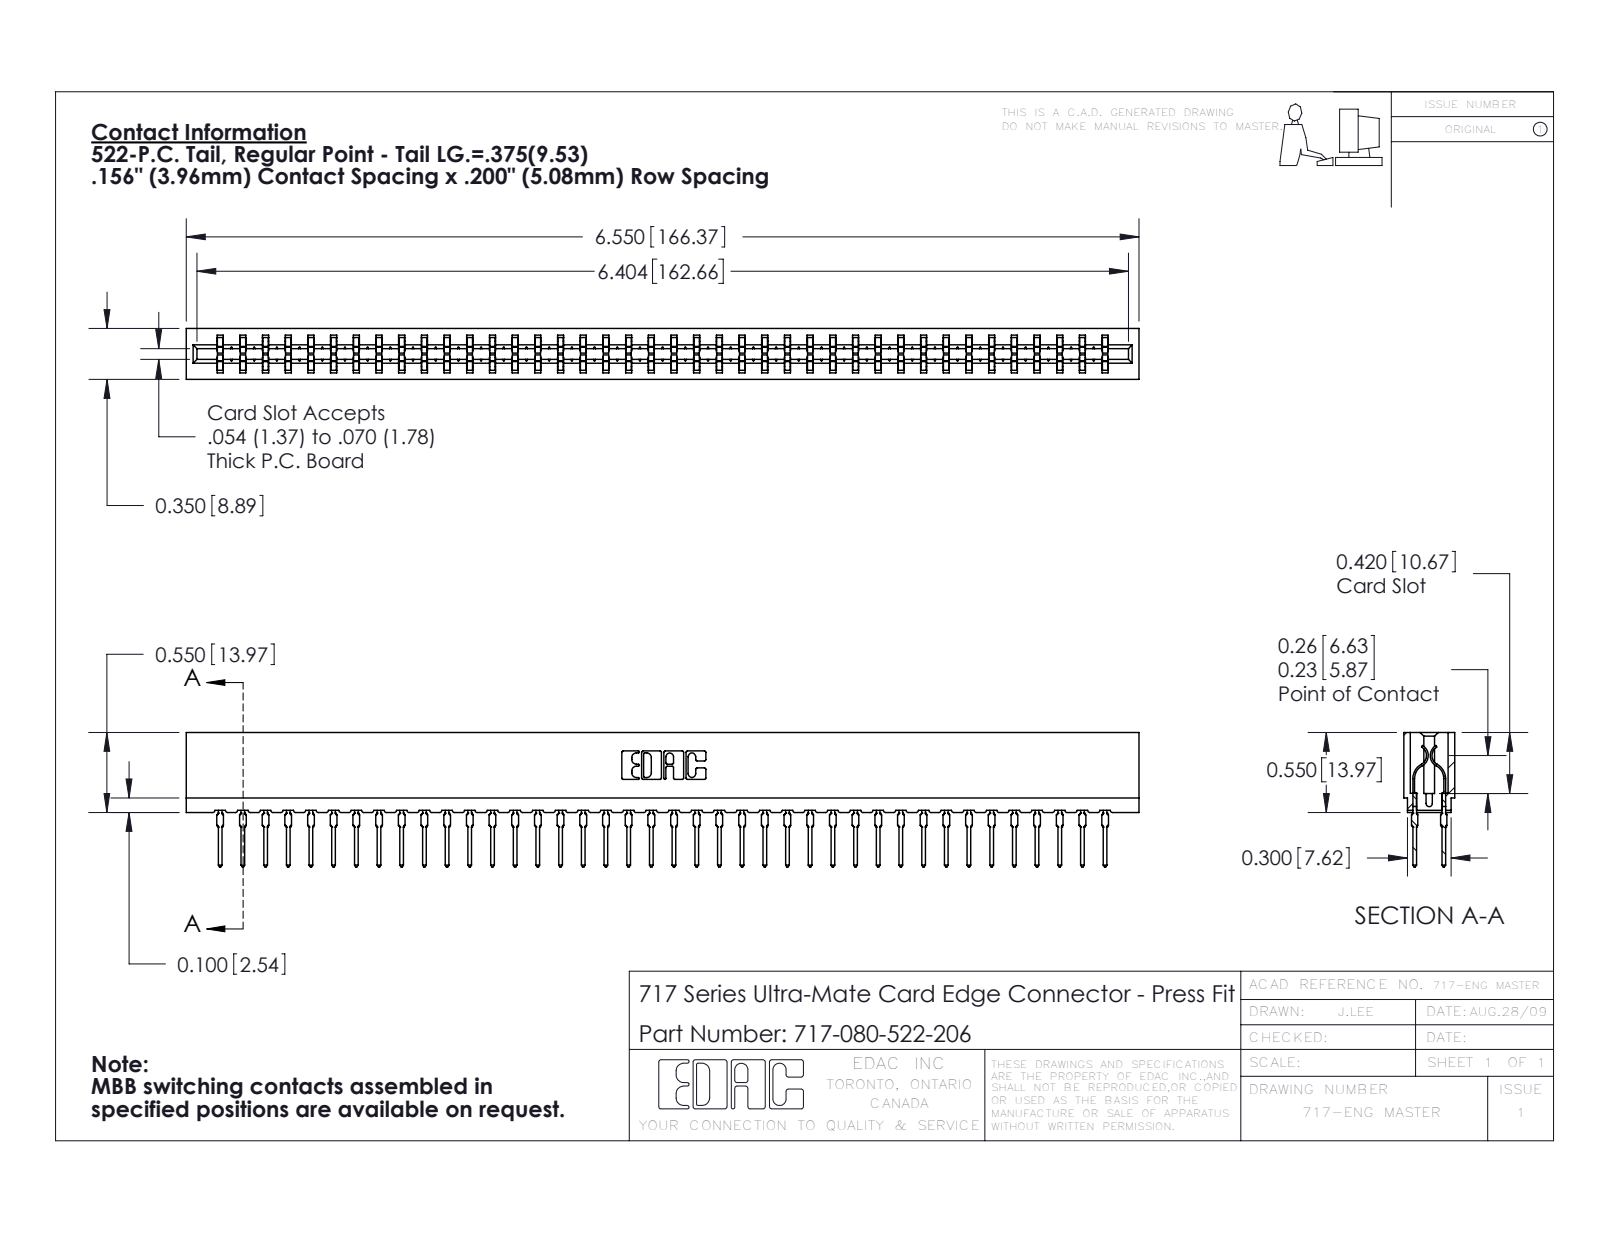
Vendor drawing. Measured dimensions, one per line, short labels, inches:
name: 717-080-522-206; 717 Part_Insulator Option - 06; 745-292-001_522
written by: SolidWorks 2016 (CONFIG_CONTROL_DESIGN)
unit: in
bodies: 81 solids, 7294 faces (3774 planar, 1440 cylindrical, 2080 other)
size: 6.55 × 0.924 × 0.35
volume: 0.885 in³; area: 34.85 in²
rounds: 160× R0.021, 80× R0.015, 22× R0.01, 8× R0.005, 8× R0.011, 6× R0.007, 6× R0.031, 3× R0.026
face distances: 0.212, 0.138, 0.35, 0.063, 0.287, 0.076, 0.149, 0.074, 0.045, 0.305
